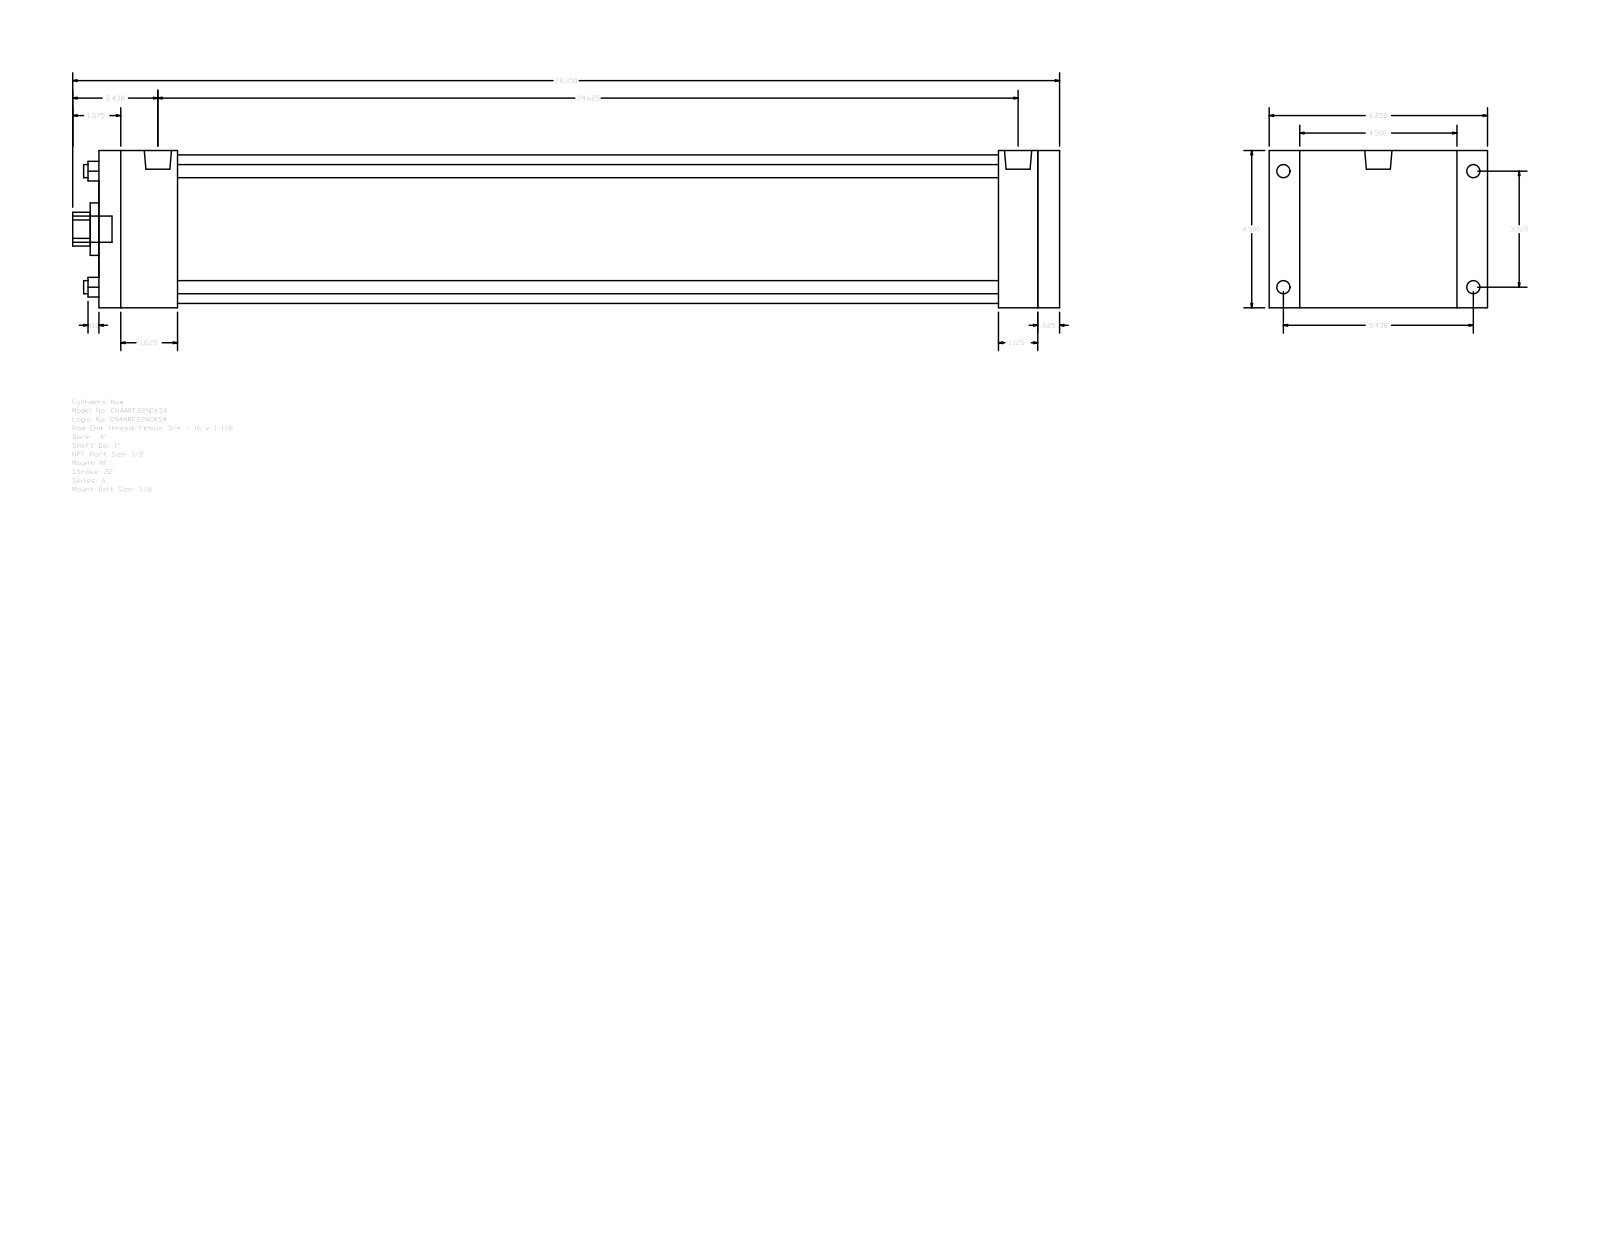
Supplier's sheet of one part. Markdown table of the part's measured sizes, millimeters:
| quantity | value |
| --- | --- |
| part name | A_RF__0400_1 |
| STEP written by | GSSL Pune (CONFIG_CONTROL_DESIGN) |
| units | millimeters |
| bodies | 0 solids, 92 faces (64 planar, 28 cylindrical, 0 other) |
| overall size | 717.55 × 158.75 × 114.3 |
| round holes (diameter × count) | 9.53 × 4, 25.4 × 1, 38.1 × 1, 107.95 × 1 |
| round bosses / shafts (diameter × count) | 9.53 × 4, 8.73 × 4, 19.77 × 2, 19.05 × 1 |
| partial cylindrical surfaces (radius × count) | 12.29 × 1 |
| main face-to-face distances | 114.3, 698.5, 682.62, 15.88, 28.57, 22.23, 136.53, 654.05, 44.45, 57.15 |
| hole center spacings | 59.62, 84.32, 119.25 |
